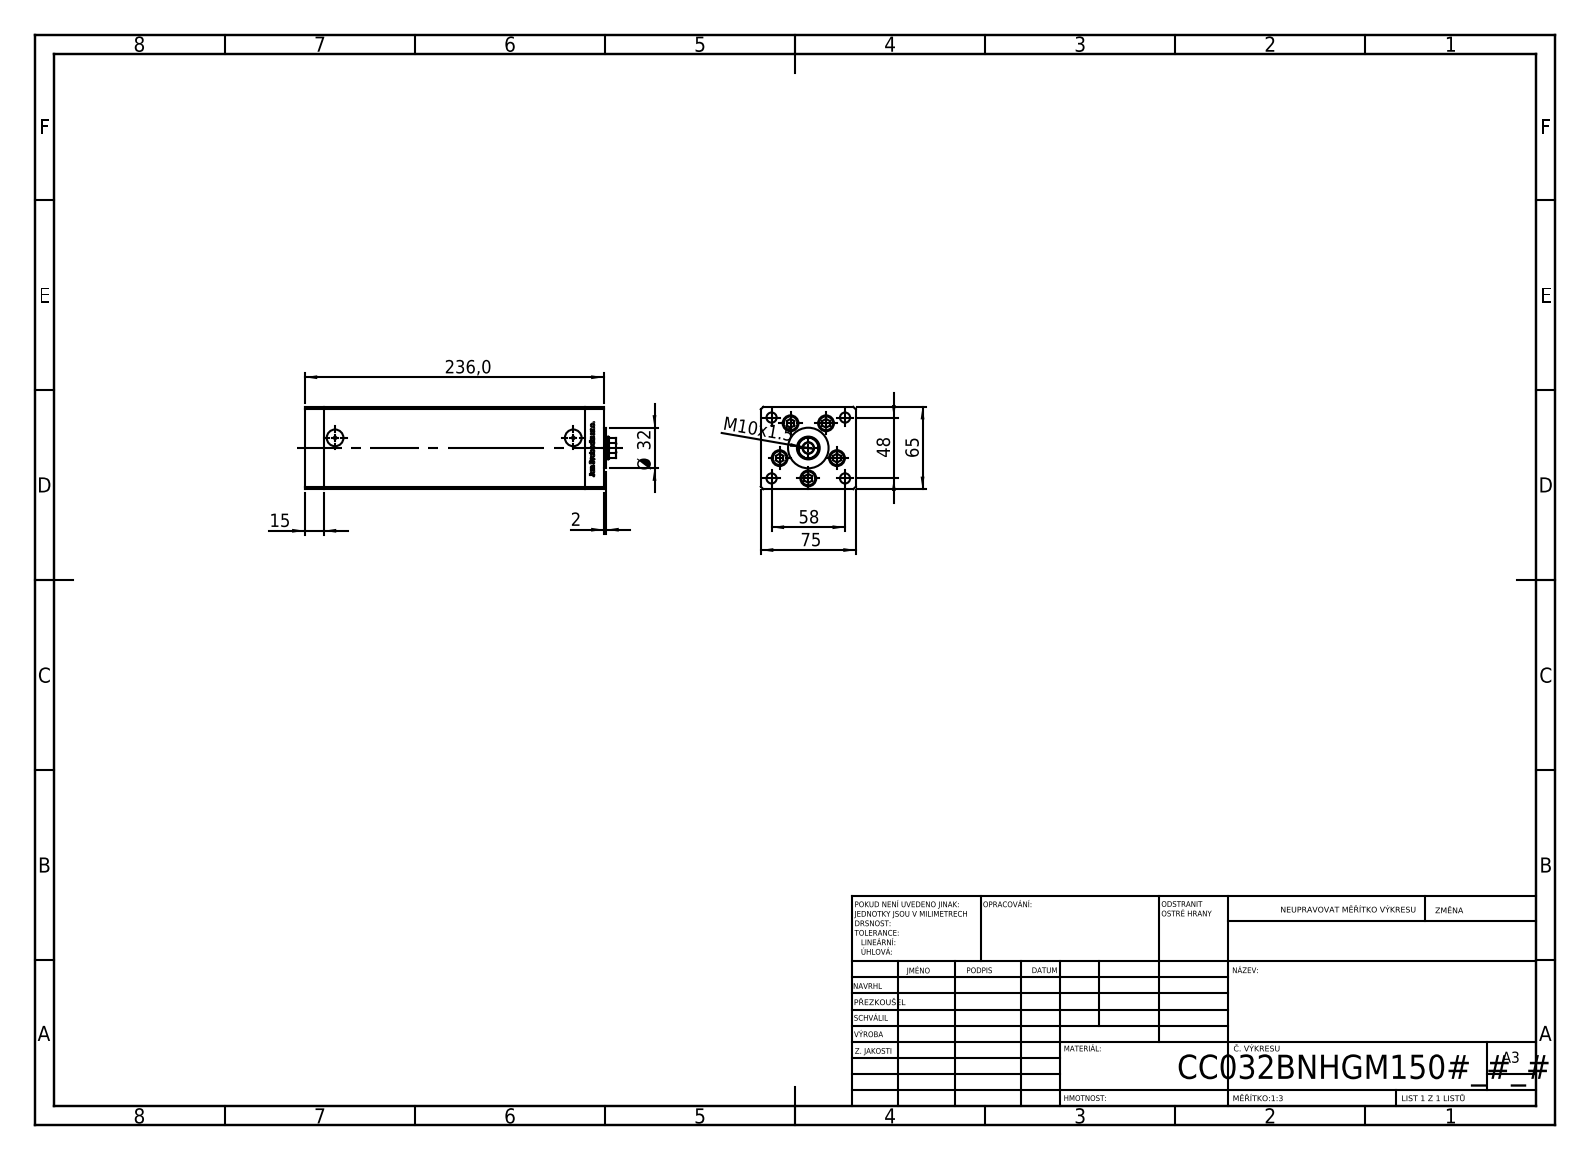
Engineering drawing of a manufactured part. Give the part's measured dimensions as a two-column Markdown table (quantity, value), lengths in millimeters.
| quantity | value |
| --- | --- |
| part name | V220C BACK_B; ALLEN BOLT; V220C_FRONT_B; V220C_VC_B (+1 more) |
| STEP written by | SolidWorks 2019 (CONFIG_CONTROL_DESIGN) |
| units | millimeters |
| bodies | 14 solids, 1183 faces (462 planar, 147 cylindrical, 574 other) |
| overall size | 246 × 75 × 65 |
| volume | 1 011 000 mm³ |
| surface area | 159 322 mm² |
| round holes (diameter × count) | 9 × 5, 12.5 × 5, 8 × 4, 2 × 2, 13.16 × 2, 8.5 × 1, 18 × 1 |
| round bosses / shafts (diameter × count) | 8 × 5, 32 × 1 |
| partial cylindrical surfaces (radius × count) | 0.93 × 2, 8.5 × 1 |
| main face-to-face distances | 75, 65, 15, 206, 221, 236, 54.5, 10.5, 26.25, 48.75 |
| hole center spacings | 24, 37.64, 15.67, 17.22, 27.71, 28.83, 29, 32.63 |
